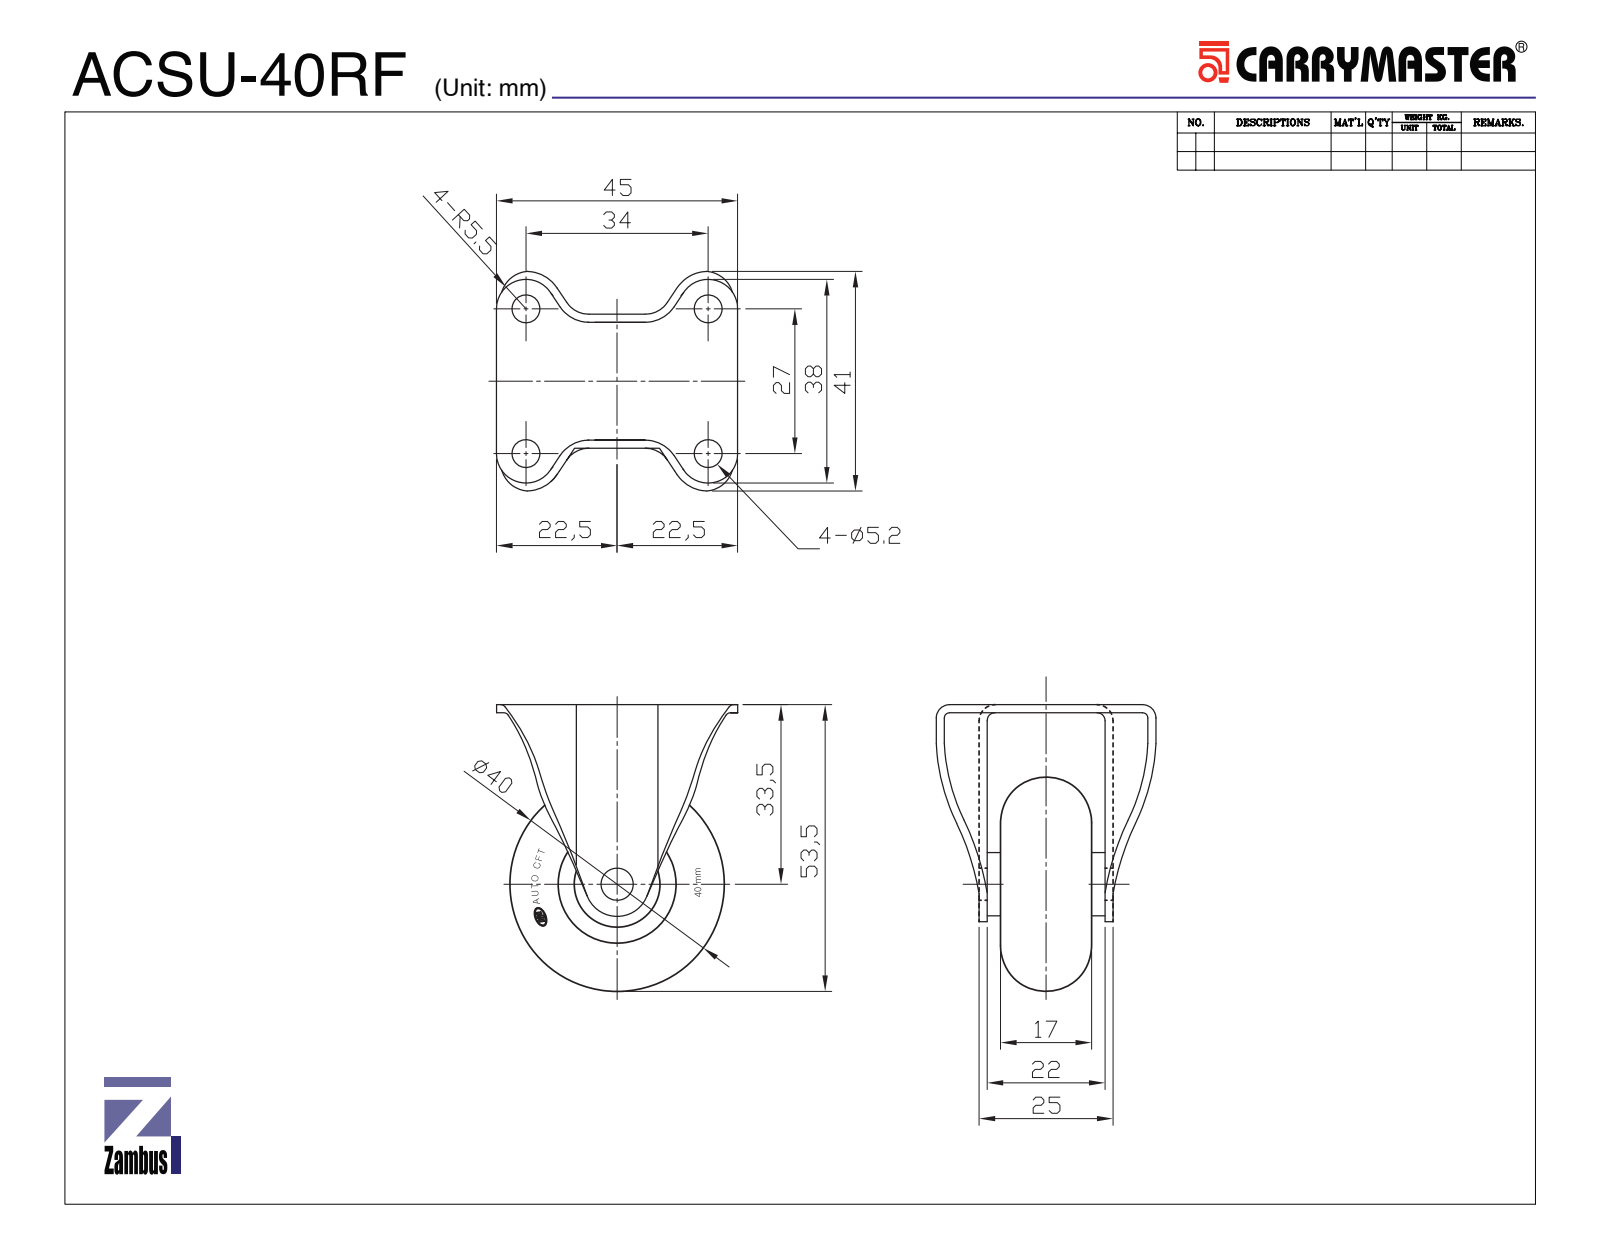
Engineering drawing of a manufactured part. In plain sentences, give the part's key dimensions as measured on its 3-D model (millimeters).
The part is named "ACSU-40RF". Its 3-D file was written by "SolidWorks 2015 (CONFIG_CONTROL_DESIGN)". It is 10 solids with 318 faces: 66 planar, 160 cylindrical and 92 other. Overall it measures 53.5 by 45 by 39.91 millimeters. Its volume is 23 944 cubic millimeters and its surface area 19 597 square millimeters. Round holes: 4 of diameter 5.2, 1 of diameter 6, 1 of diameter 8, 1 of diameter 10.35, 1 of diameter 13, 1 of diameter 13.75, 1 of diameter 16, 1 of diameter 22. Round bosses or shafts: 1 of diameter 29, 1 of diameter 16, 1 of diameter 10.5, 1 of diameter 10.25, 1 of diameter 9. Partial cylindrical surfaces (rounded edges, fillets, slot ends): 36 of radius 1, 4 of radius 2.5, 4 of radius 5, 4 of radius 6.25, 4 of radius 6.5, 4 of radius 10.32, 4 of radius 11.82, 1 of radius 6. The main face-to-face distances are 1.5, 19.5, 4, 21, 23.5, 2.5, 17, 25, 22, 5. The hole center spacings are 27, 34, 43.42.
